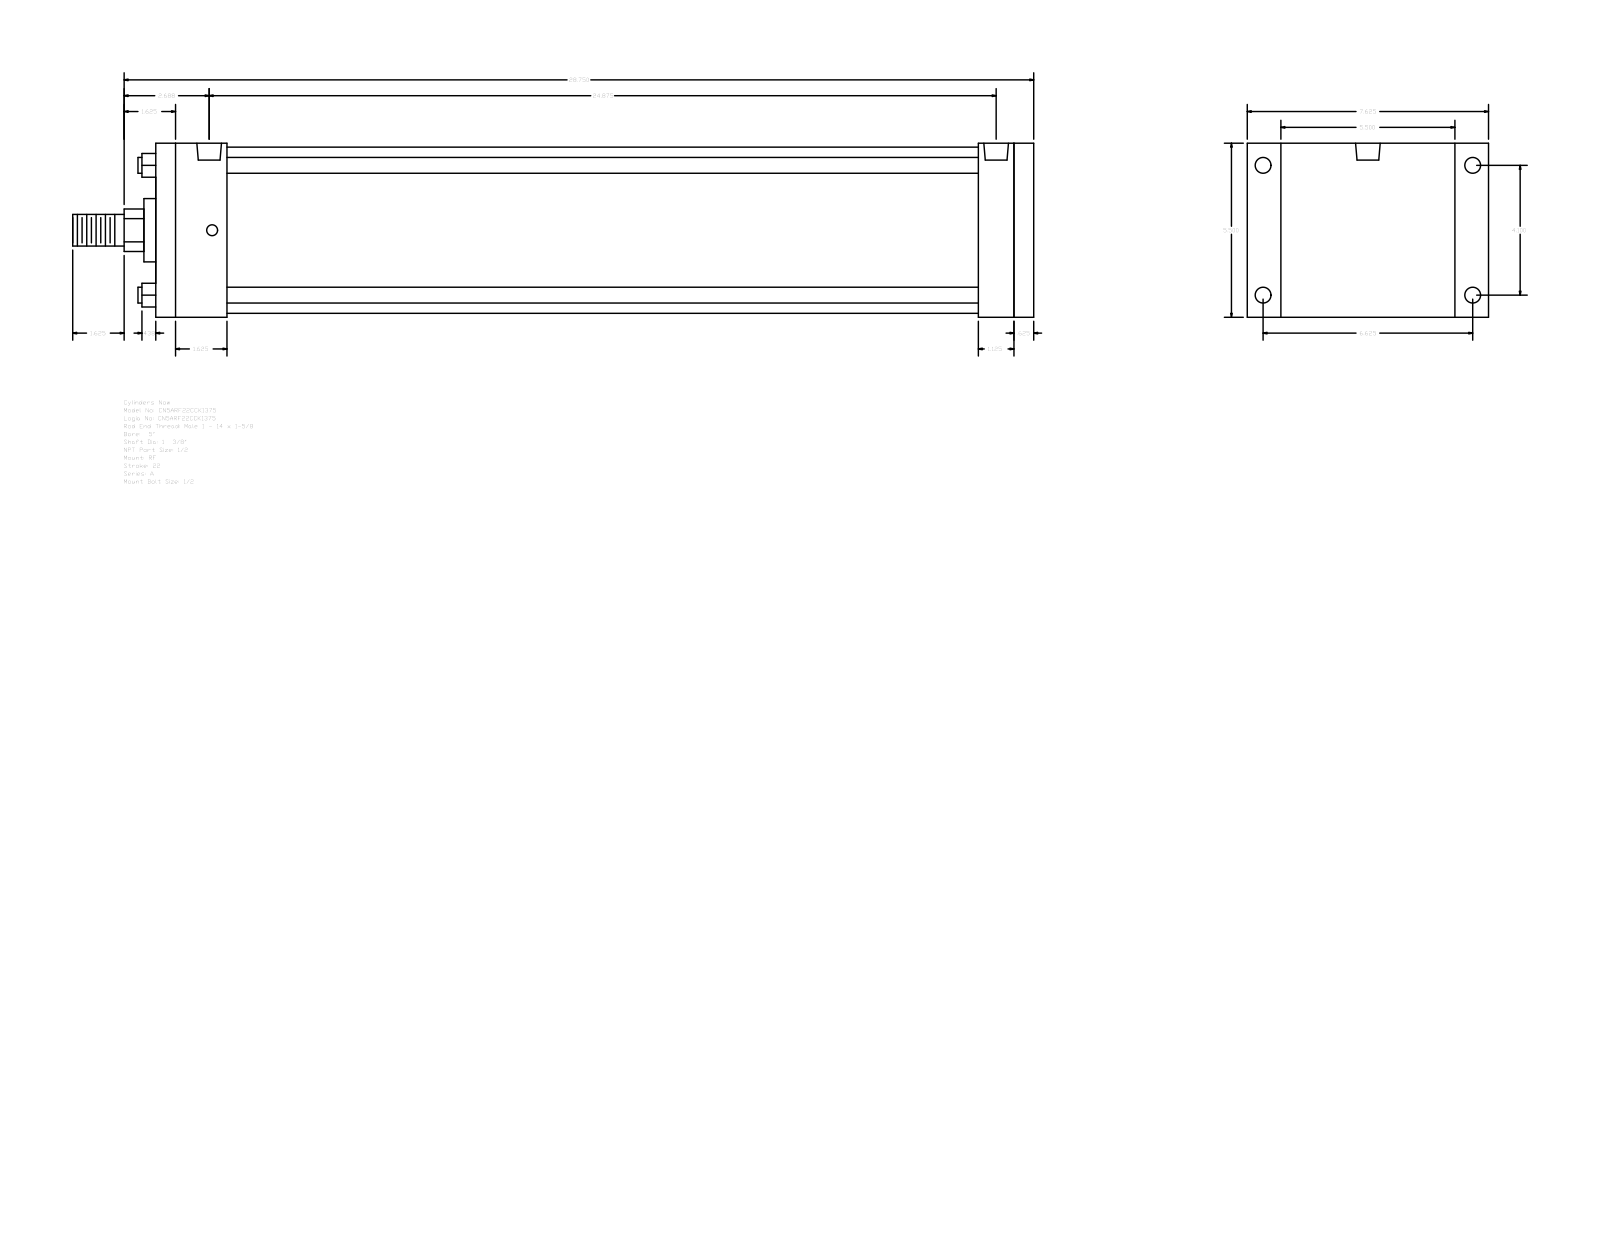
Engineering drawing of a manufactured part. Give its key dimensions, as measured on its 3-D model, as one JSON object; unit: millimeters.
{"part_name": "A_RF__0500_1.375", "step_written_by": "GSSL Pune (CONFIG_CONTROL_DESIGN)", "units": "millimeters", "bodies": {"solids": 0, "faces": 92, "planar": 64, "cylindrical": 28, "other": 0}, "overall_size": [771.52, 193.68, 139.7], "round_holes": [[8.73, 4], [12.7, 4], [19.77, 2]], "round_bosses_or_shafts": [[12.7, 4], [133.35, 1], [50.8, 1], [34.92, 1], [25.4, 1]], "partial_cylinders_radius": [[17.06, 1]], "face_to_face_distances": [139.7, 704.85, 688.98, 15.87, 57.15, 28.58, 631.83, 647.7, 660.4, 603.25], "hole_center_spacings": [2.39, 104.14, 168.28, 197.9, 627.05, 629.44, 631.83]}
